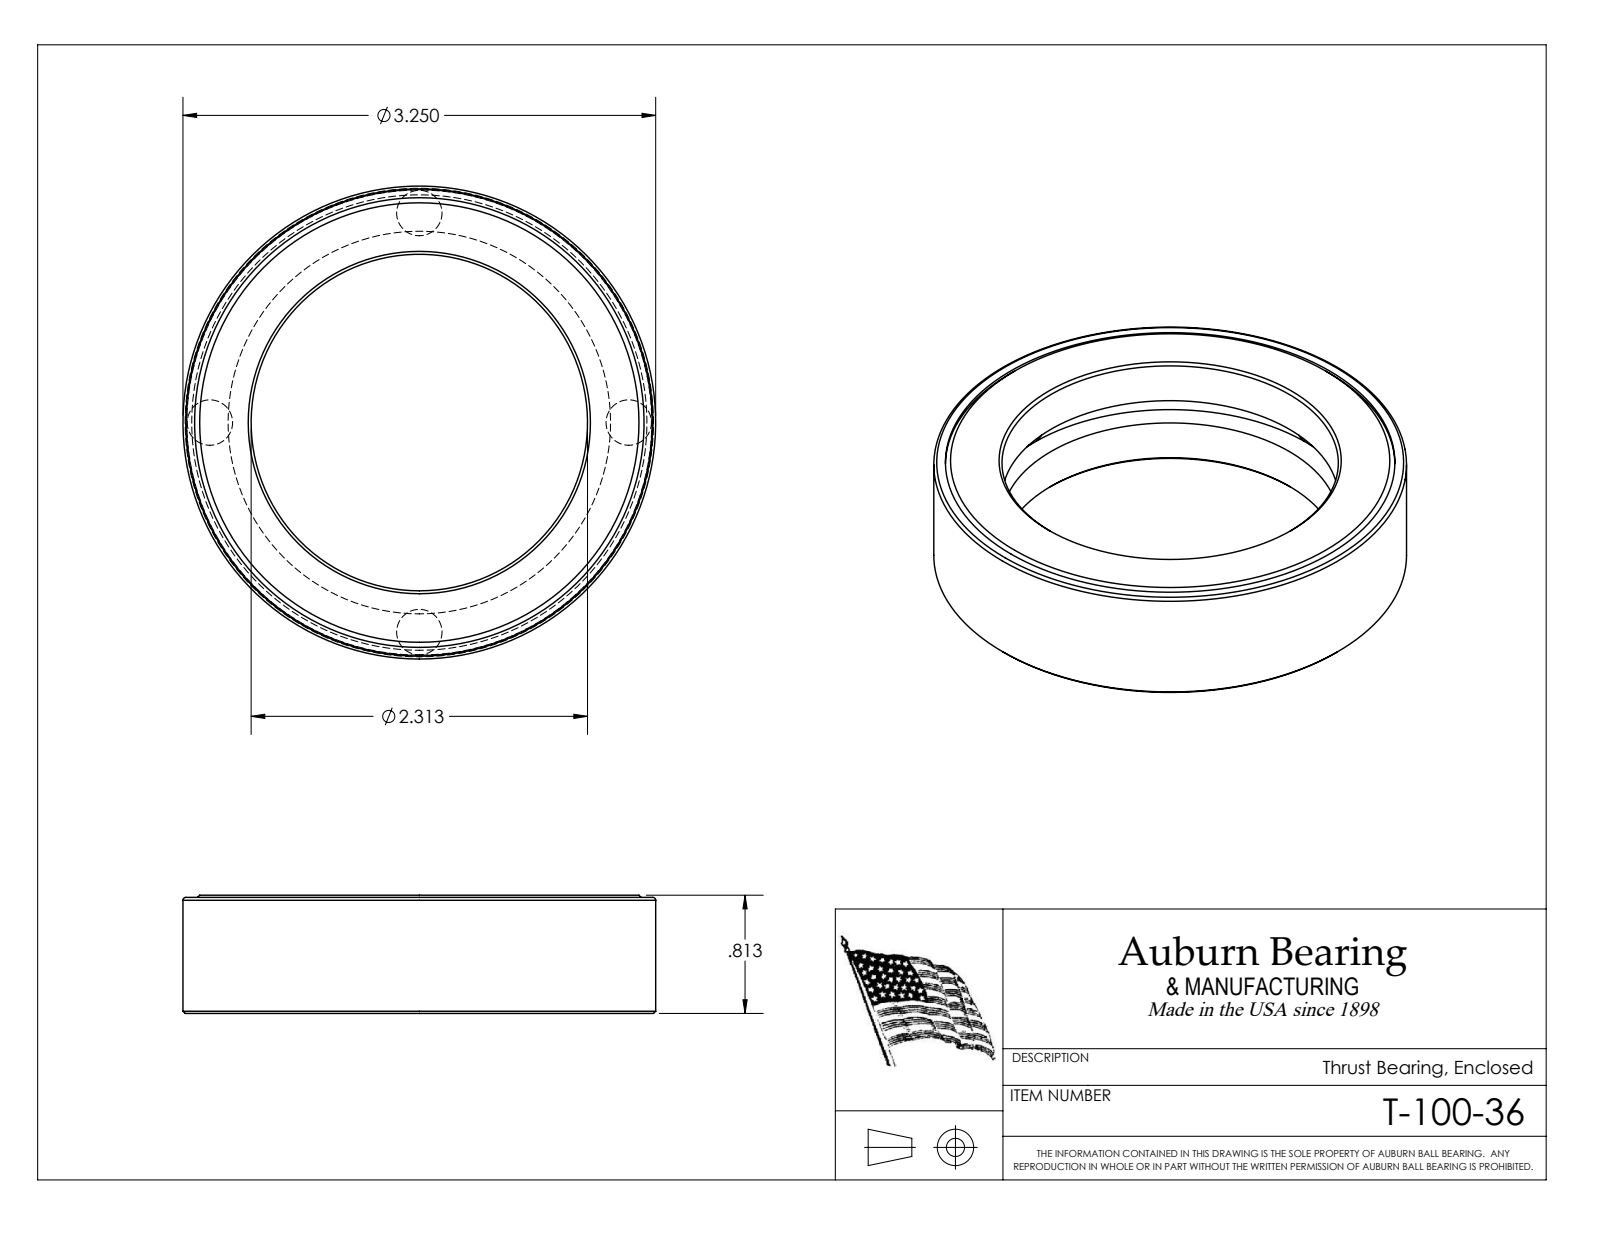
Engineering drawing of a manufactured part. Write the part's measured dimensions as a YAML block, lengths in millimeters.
part_name: "T-100-36"
step_written_by: "SolidWorks 2016 (CONFIG_CONTROL_DESIGN)"
units: millimeters
bodies: {solids: 6, faces: 28, planar: 9, cylindrical: 7, other: 12}
overall_size: [82.6, 82.6, 20.7]
volume: 39460
surface_area: 25080
round_holes:
  - {diameter: 58.8, count: 1}
  - {diameter: 78.5, count: 1}
  - {diameter: 81.5, count: 1}
round_bosses_or_shafts:
  - {diameter: 82.6, count: 1}
  - {diameter: 81.2, count: 1}
face_to_face_distances: [8, 12.7, 20.7, 4.7, 20.3, 12.3, 7.6, 0.4, 19.8, 11.8]
